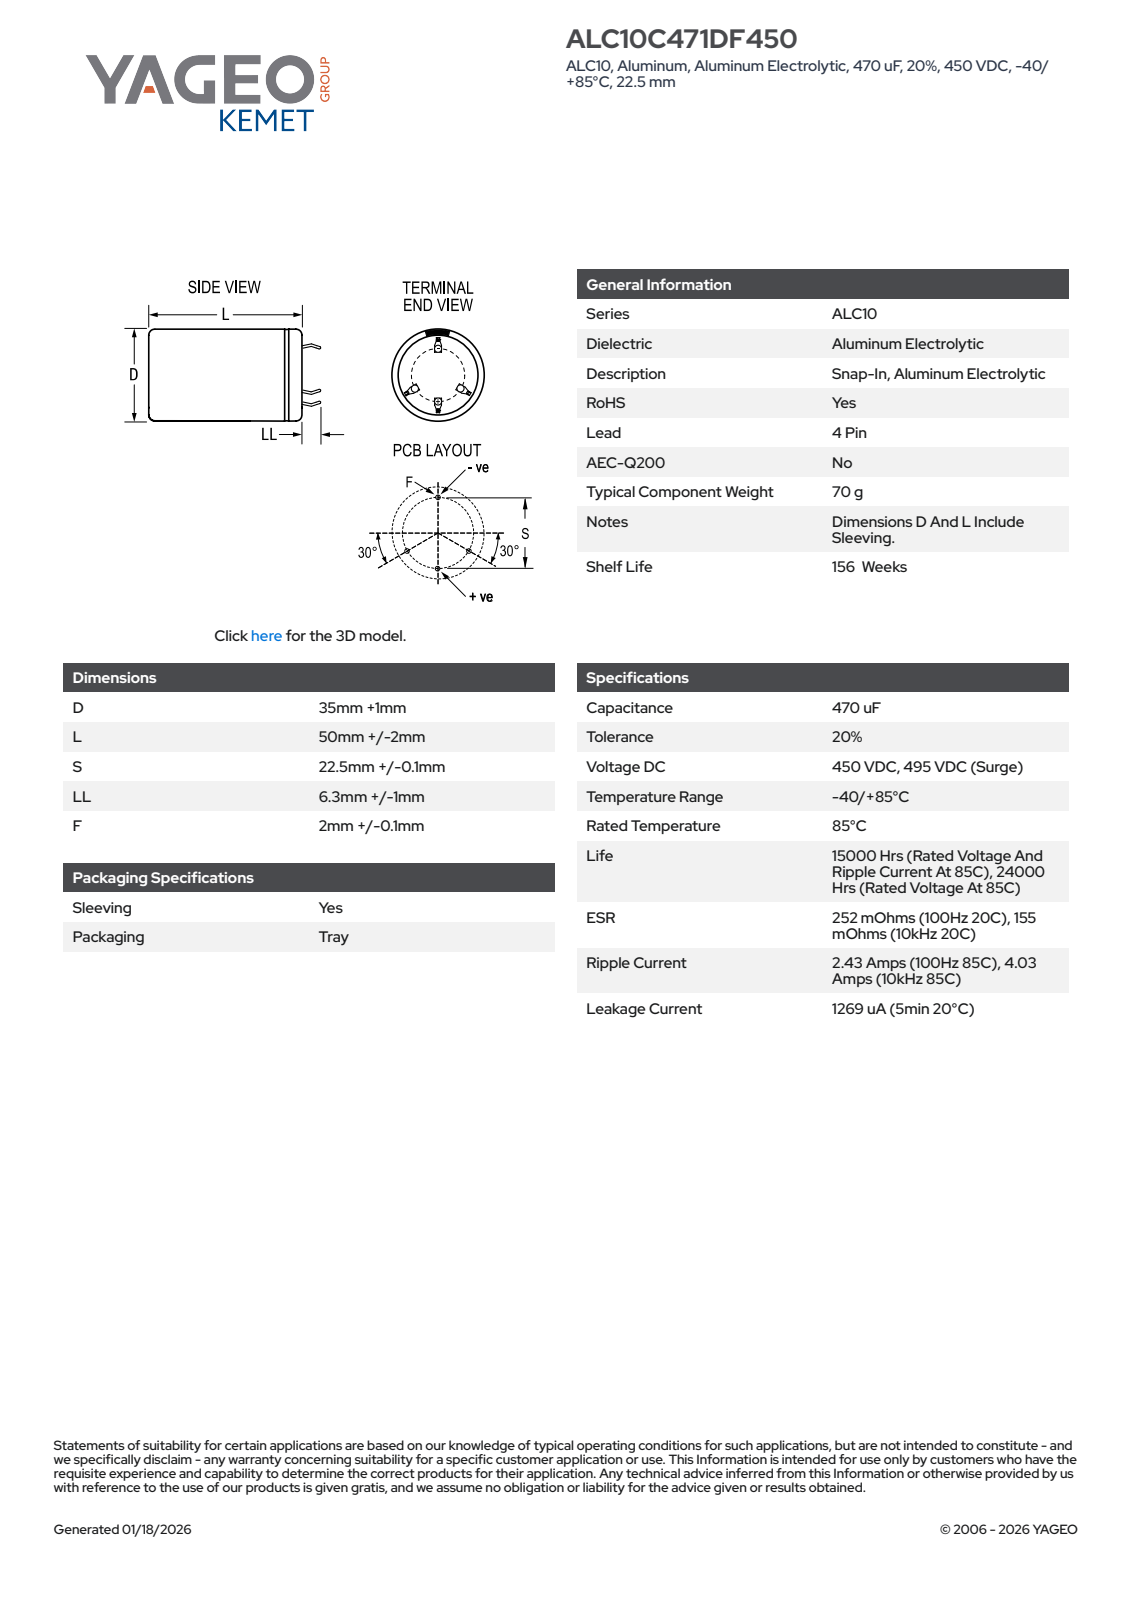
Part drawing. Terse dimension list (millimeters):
name: CARS_K4P_35X50_D36L52S22.5LL7.3F2.1
written by: SolidWorks 2014 (AUTOMOTIVE_DESIGN)
unit: mm
bodies: 1 solid, 134 faces (80 planar, 15 cylindrical, 39 other)
size: 59.29 × 36 × 36
volume: 52 415 mm³; area: 7 962 mm²
holes: 1× ⌀31.85
bosses: 1× ⌀36
rounds: 1× R17.99
face distances: 51.99, 52.49, 0.5, 0.6, 0.55, 0.75, 1.35, 2.1, 23.36, 22.81
